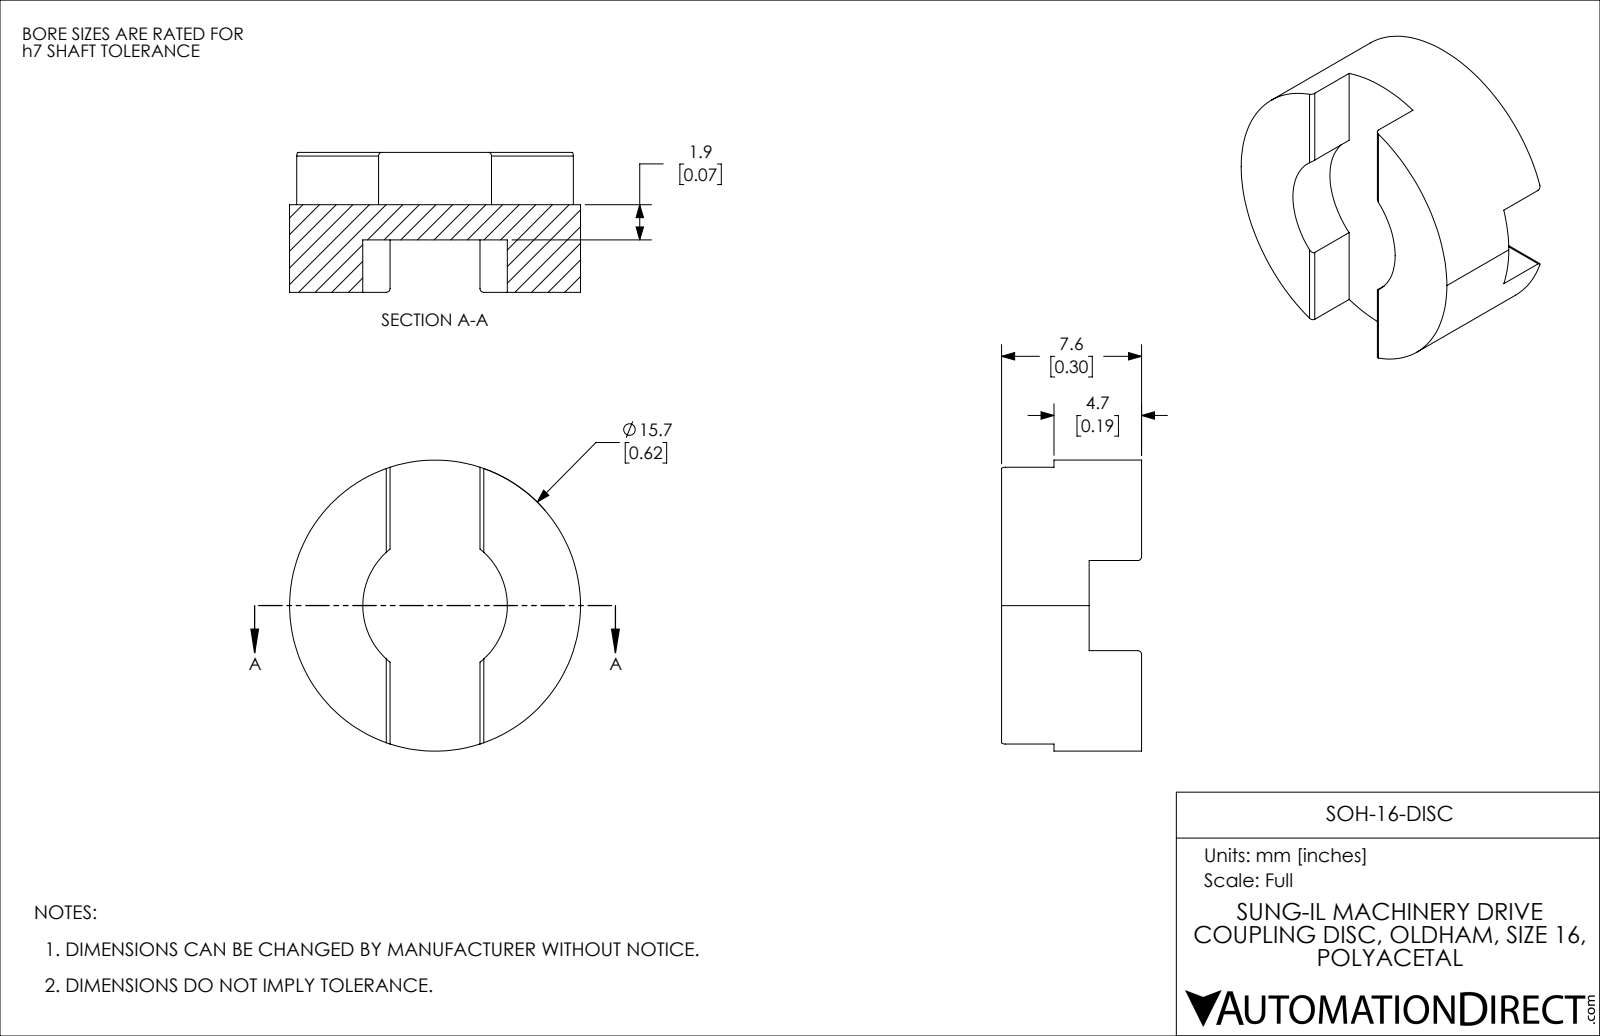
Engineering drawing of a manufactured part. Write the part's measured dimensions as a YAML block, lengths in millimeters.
part_name: "SOH-16-DISC"
step_written_by: "SolidWorks 2021 (CONFIG_CONTROL_DESIGN)"
units: millimeters
bodies: {solids: 1, faces: 29, planar: 14, cylindrical: 15, other: 0}
overall_size: [15.7, 15.7, 7.55]
volume: 967
surface_area: 879
round_holes:
  - {diameter: 7.8, count: 1}
round_bosses_or_shafts:
  - {diameter: 15.7, count: 1}
partial_cylinders:
  - {radius: 0.2, count: 4}
face_to_face_distances: [2.83, 4.73, 7.56, 1.9, 4.86]
